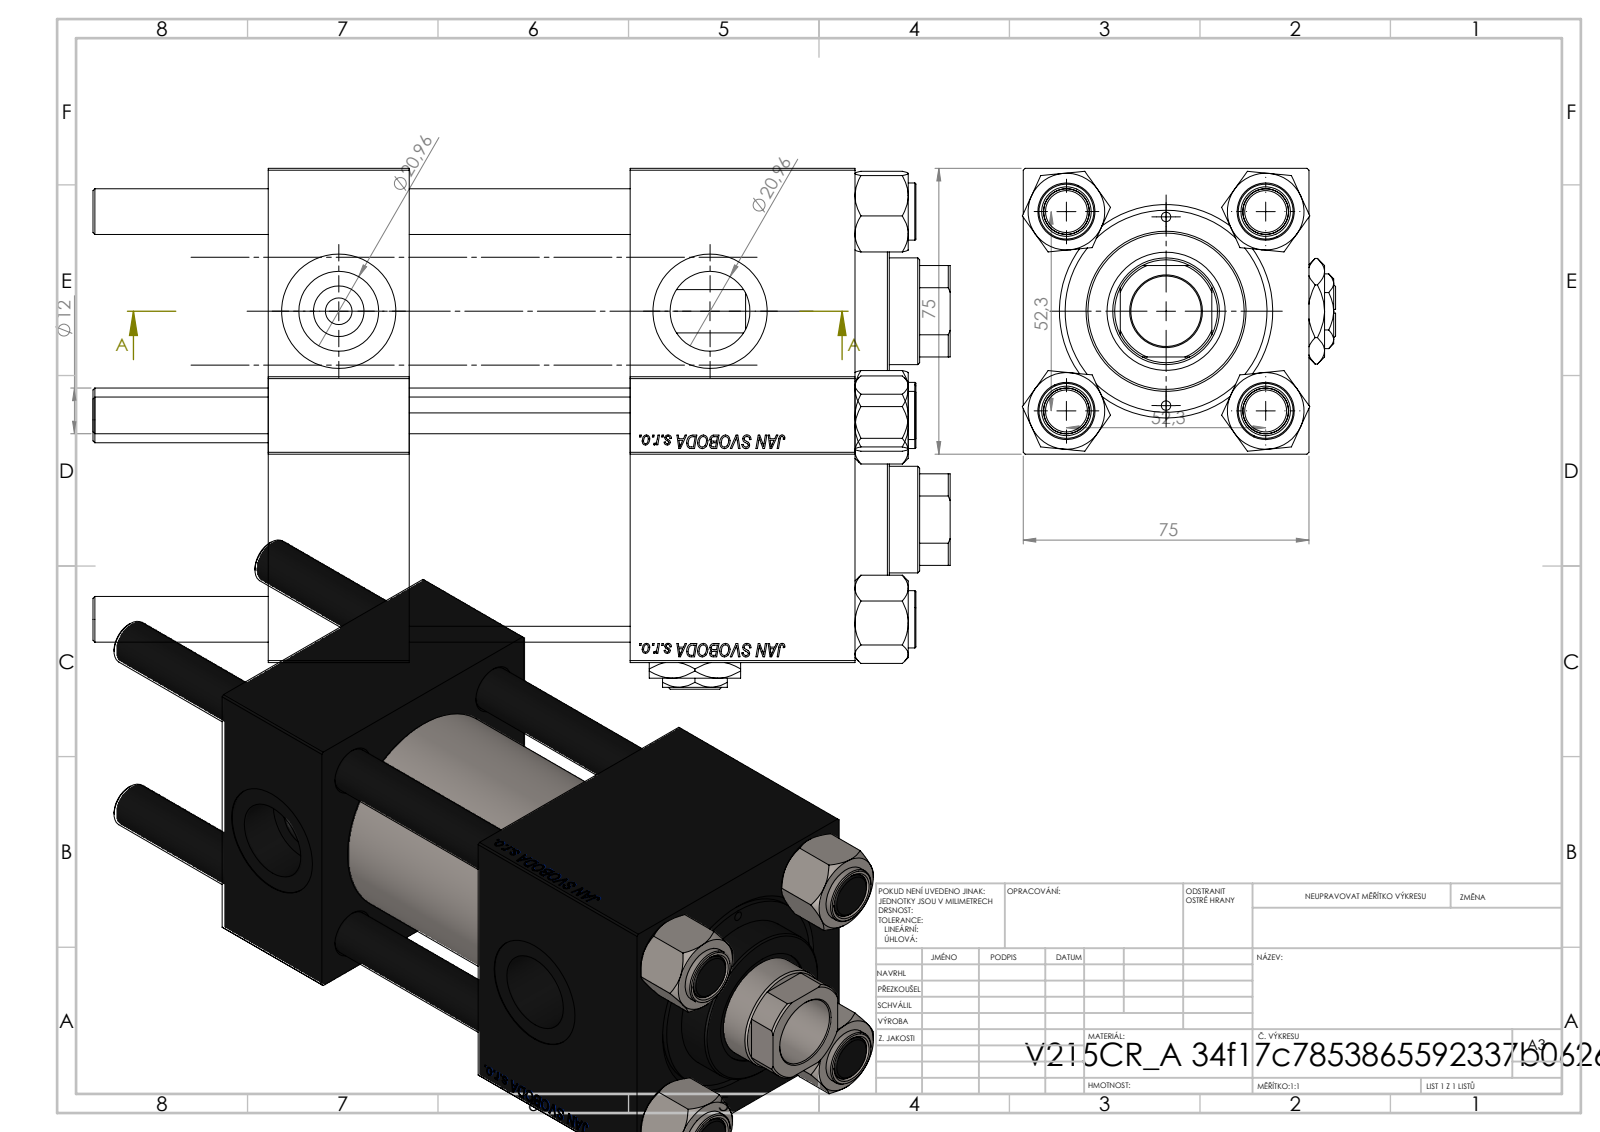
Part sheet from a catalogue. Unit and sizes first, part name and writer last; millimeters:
Units: millimetres
Overall size (bounding box): 225 × 82.22 × 75
Round holes (diameter × count): ⌀12 ×4, ⌀20.96 ×3, ⌀30 ×3, ⌀2.5 ×2, ⌀7 ×2, ⌀18.5 ×1, ⌀28 ×1, ⌀31 ×1, ⌀41 ×1, ⌀50 ×1, ⌀53 ×1
Round bosses / shafts (diameter × count): ⌀15 ×4, ⌀56 ×1, ⌀42 ×1
Partial cylindrical surfaces — rounded edges, fillets, slot ends (radius × count): R13.5 ×1
Main face-to-face distances: 75, 37, 154, 117, 95, 59, 58, 125.3, 88.3, 30.3
Hole centre spacings: 26.19, 36.98, 52.3, 57.22, 24.75, 73.96, 3.96, 49.5
Volume: 697 723 mm³ · Surface area: 169 209 mm²
Bodies: 12 solids, 1188 faces (545 planar, 87 cylindrical, 556 other)
Part name (STEP PRODUCT): CR025_012_A_0_G_A_G_M_020_+#_##_TYCINKA; V215CR_VCP; Zatka_pro_OIL_PORT; NUT_M5 (+2 more)
STEP written by: SolidWorks 2019 (CONFIG_CONTROL_DESIGN)
